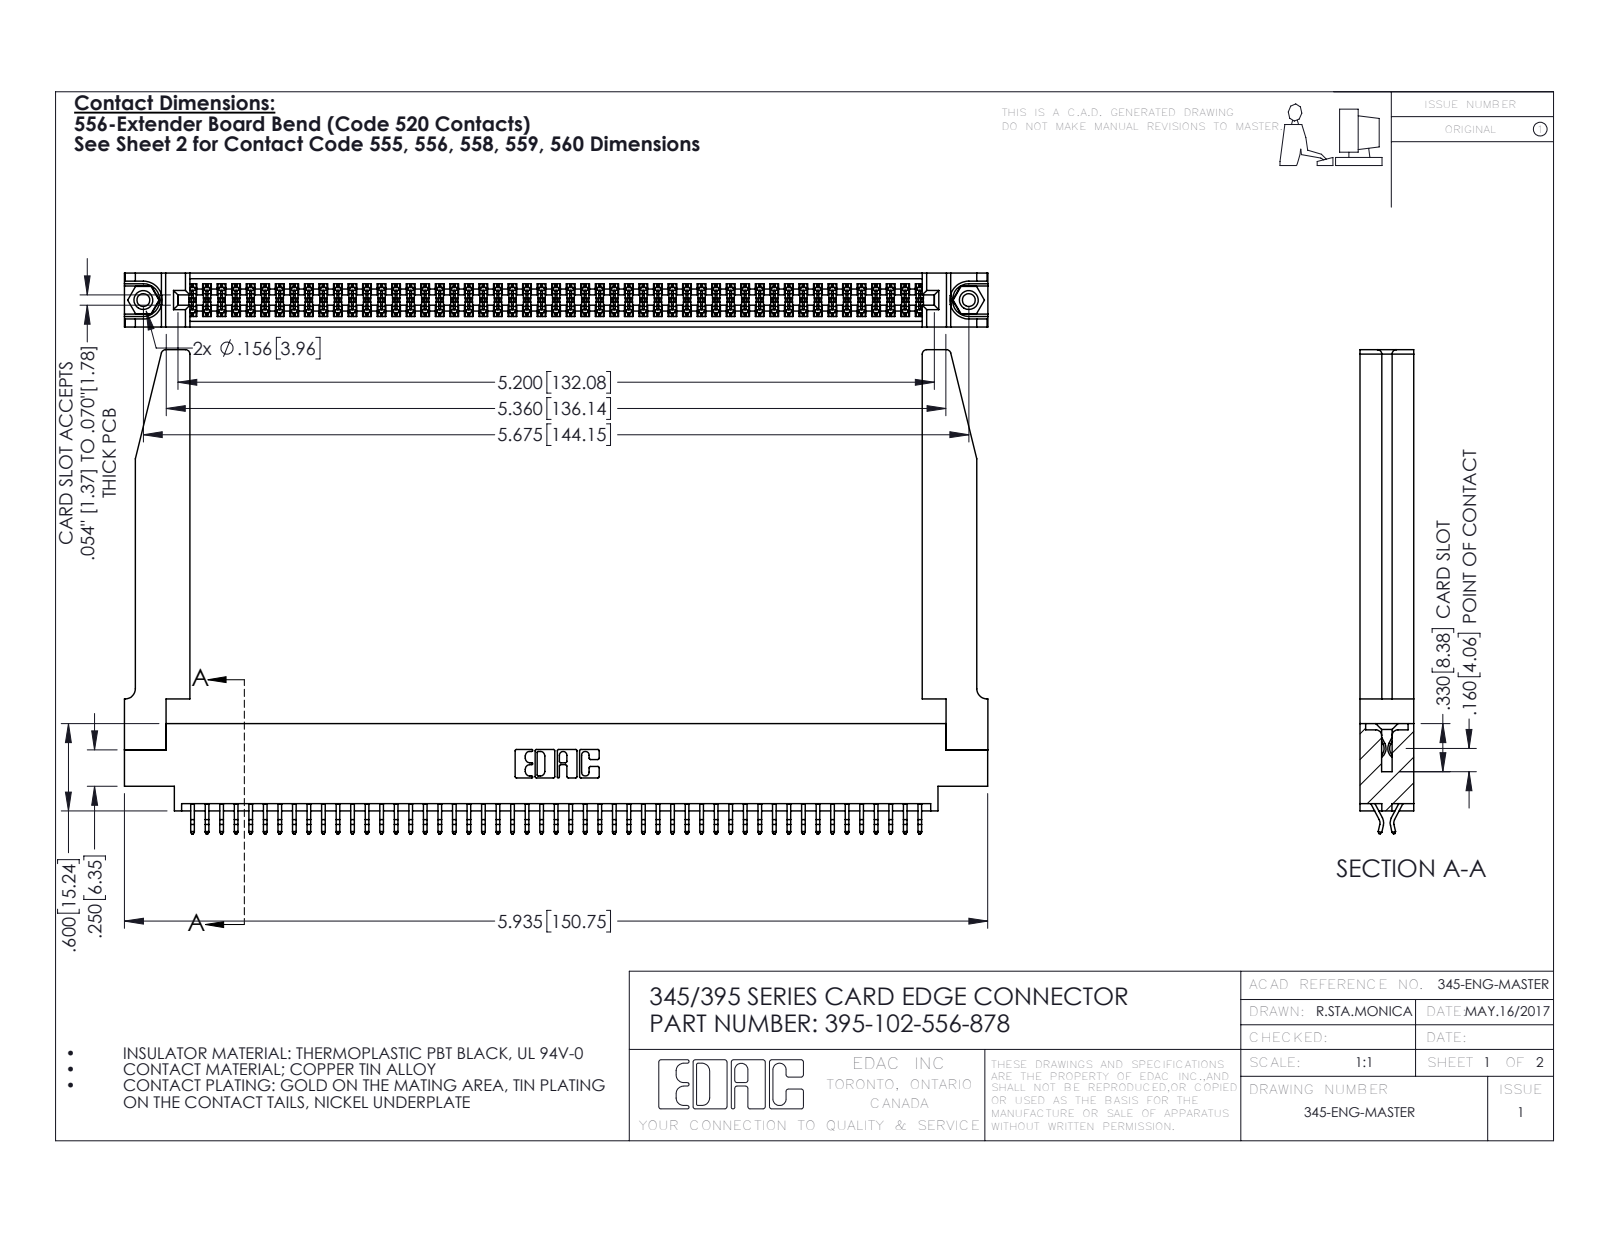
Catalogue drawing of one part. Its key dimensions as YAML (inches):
part_name: "395-102-556-878; 345-292-001_556 Tail; 345-250-001_345-250-001-102; 345 Part_0.170 Offset - 0.156 Dia-TH (+1 more)"
step_written_by: "SolidWorks 2016 (CONFIG_CONTROL_DESIGN)"
units: inches
bodies: {solids: 107, faces: 6076, planar: 4000, cylindrical: 2024, other: 52}
overall_size: [5.936, 3.327, 0.37]
volume: 1.366
surface_area: 44.43
round_holes:
  - {diameter: 0.089, count: 2}
  - {diameter: 0.125, count: 2}
  - {diameter: 0.156, count: 2}
  - {diameter: 0.064, count: 1}
round_bosses_or_shafts:
  - {diameter: 0.155, count: 2}
partial_cylinders:
  - {radius: 0.006, count: 153}
  - {radius: 0.01, count: 22}
  - {radius: 0.03, count: 8}
  - {radius: 0.007, count: 6}
  - {radius: 0.031, count: 6}
  - {radius: 0.026, count: 3}
  - {radius: 0.01, count: 2}
  - {radius: 0.014, count: 2}
face_to_face_distances: [0.37, 0.072, 0.298, 0.025, 0.098, 0.272, 0.2, 0.225, 0.175, 0.148]
hole_center_spacings: [0.27, 5.439, 5.675]
